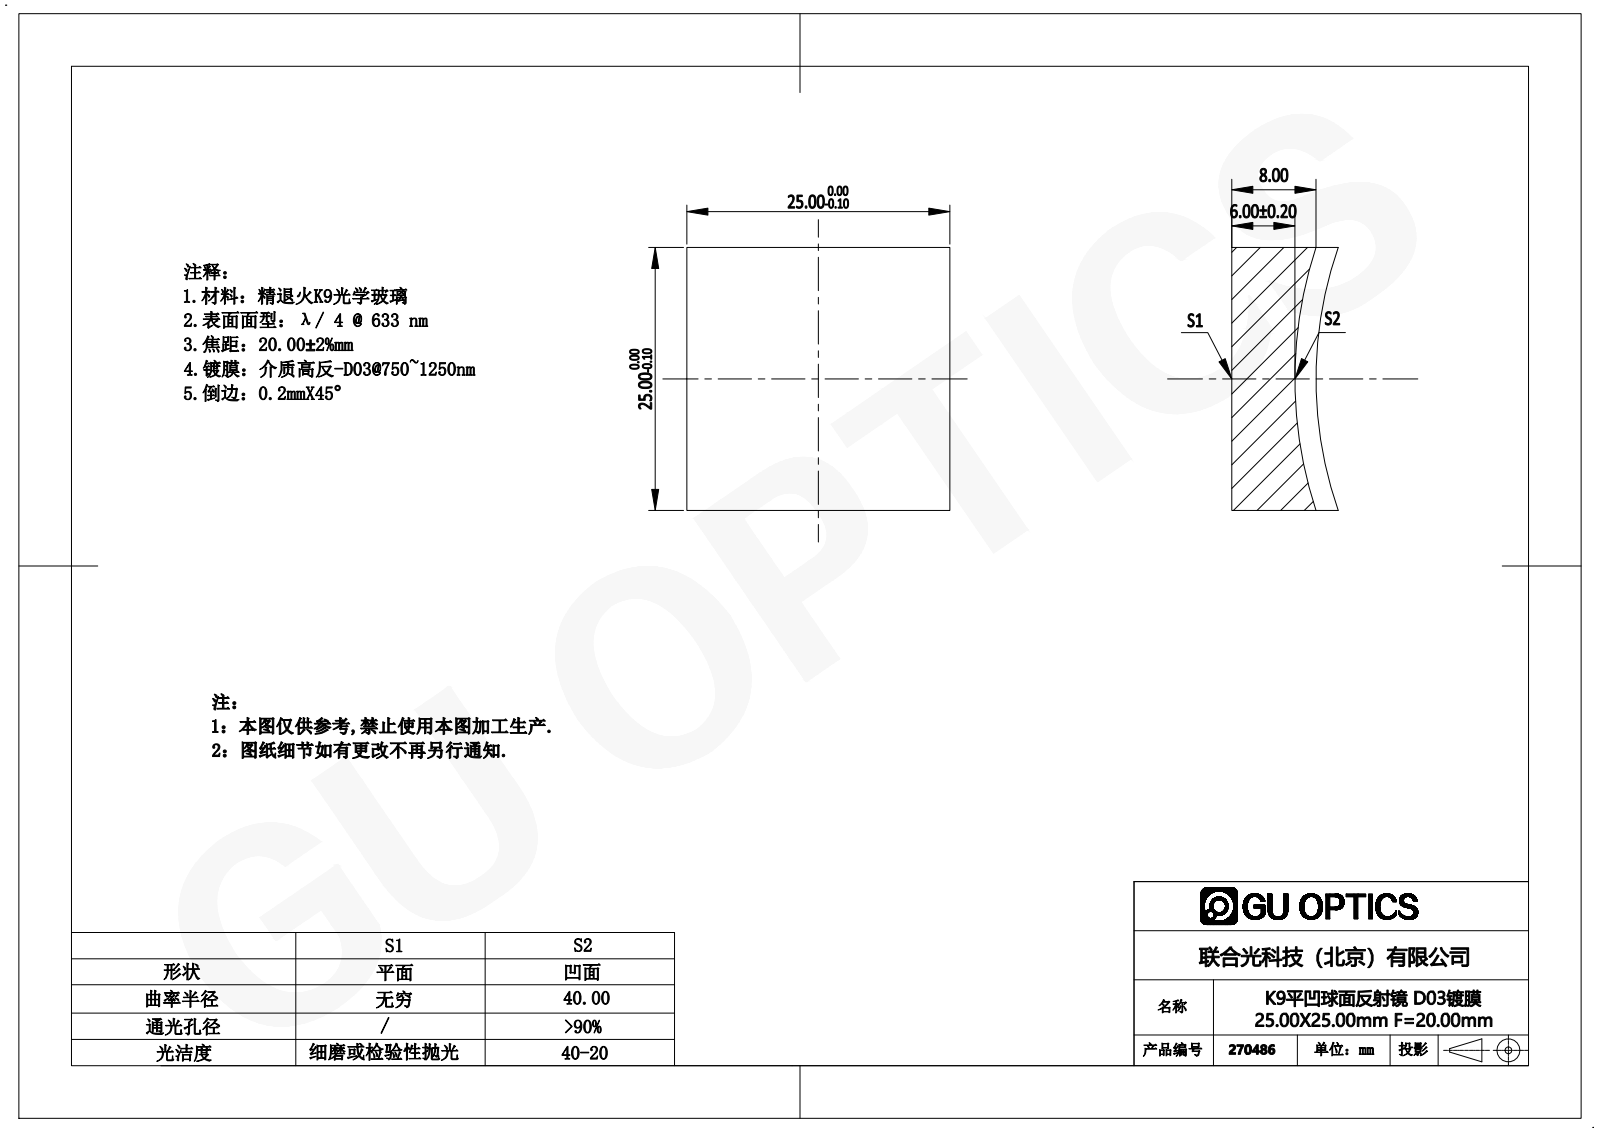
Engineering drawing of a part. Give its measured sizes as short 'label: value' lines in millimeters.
name: 270031
written by: SolidWorks 2019 (AUTOMOTIVE_DESIGN)
unit: mm
bodies: 1 solid, 7 faces (5 planar, 0 cylindrical, 2 other)
size: 25 × 25 × 10.12
volume: 4 583 mm³; area: 2 142 mm²
face distances: 25
